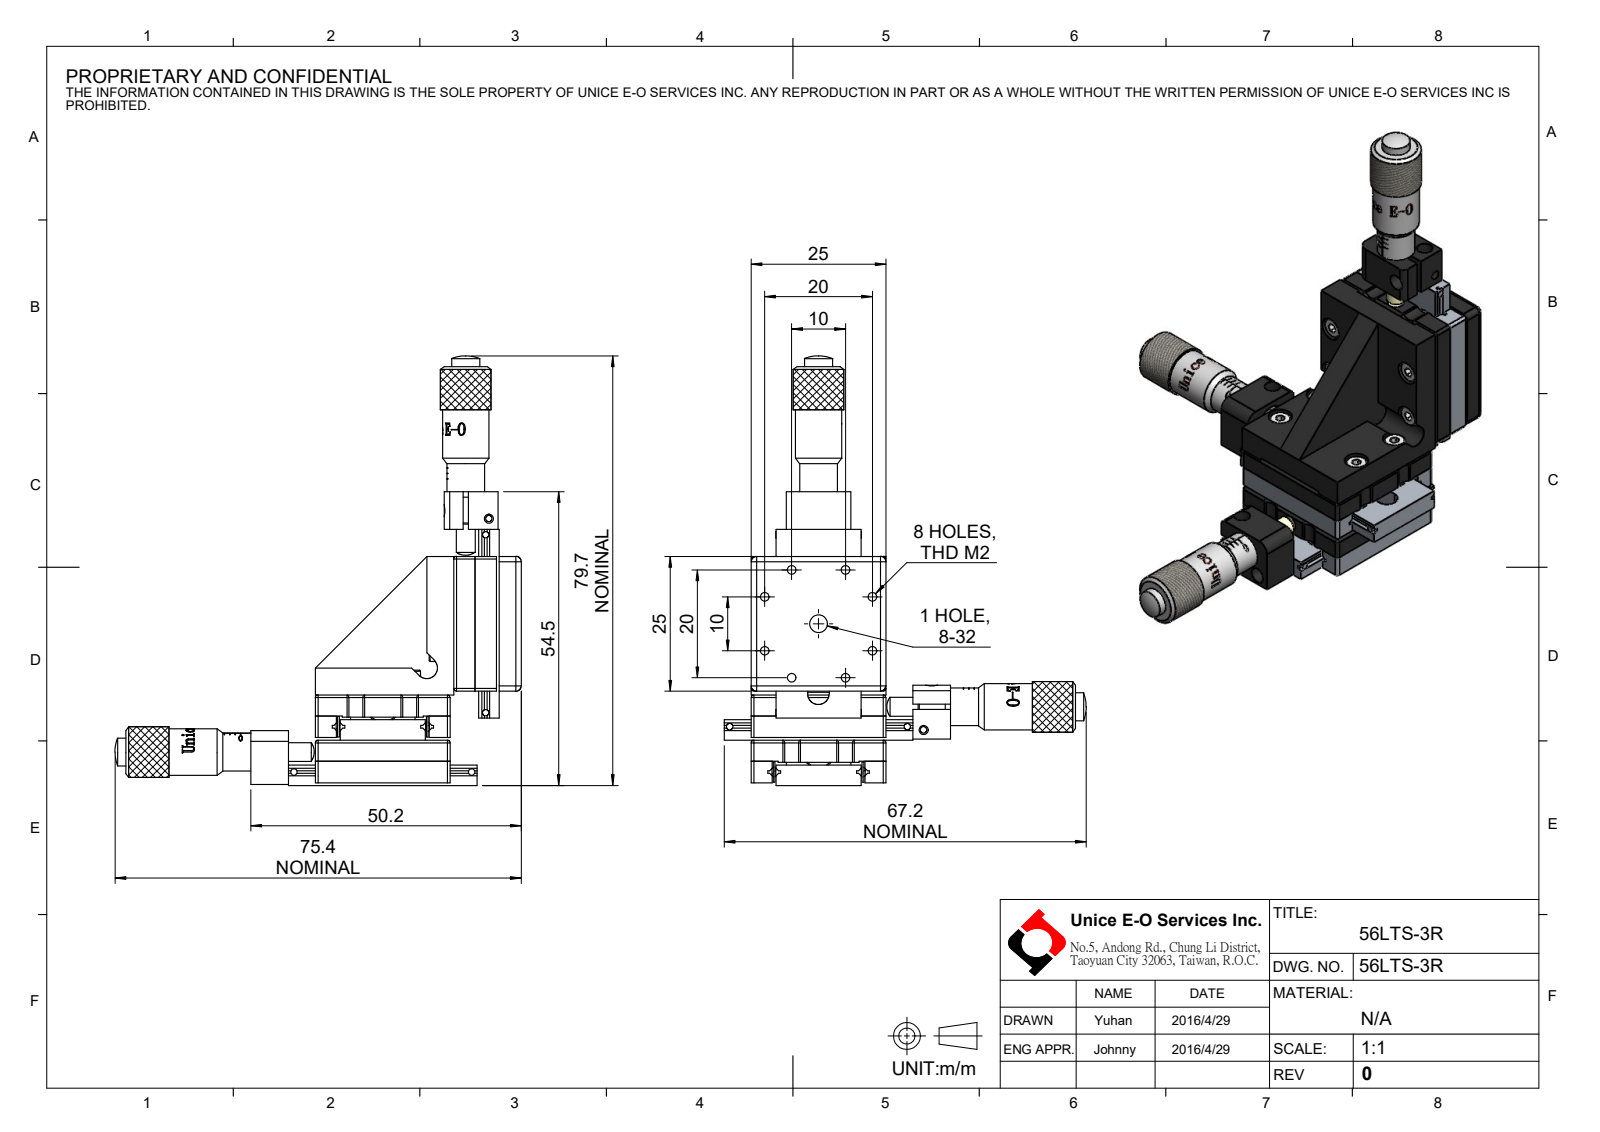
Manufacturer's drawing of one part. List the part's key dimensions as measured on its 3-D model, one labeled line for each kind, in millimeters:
Part name (STEP PRODUCT): 56LTS-3R
STEP written by: SolidWorks 2016 (CONFIG_CONTROL_DESIGN)
Units: millimetres
Bodies: 73 solids, 2750 faces (1124 planar, 1026 cylindrical, 600 other)
Overall size (bounding box): 79.7 × 75.4 × 67.2
Volume: 28 678 mm³ · Surface area: 30 420 mm²
Round holes (diameter × count): ⌀1.1 ×30, ⌀1.8 ×27, ⌀3.1 ×18, ⌀1.6 ×16, ⌀2.4 ×16, ⌀1.2 ×12, ⌀3 ×12, ⌀4 ×12, ⌀4.4 ×8, ⌀1.7 ×3, ⌀2.5 ×3, ⌀2.6 ×3
Round bosses / shafts (diameter × count): ⌀1.5 ×35, ⌀2 ×8, ⌀4 ×4, ⌀9.4 ×3, ⌀8.6 ×3, ⌀7 ×3, ⌀6.4 ×3, ⌀5.7 ×3
Partial cylindrical surfaces — rounded edges, fillets, slot ends (radius × count): R0.5 ×44, R2 ×22, R0.75 ×14, R1 ×11, R4.28 ×3
Main face-to-face distances: 8.4, 4.6, 0.5, 8.9, 4.5, 0.7, 4.1, 4.3, 3.8, 3.9
Hole centre spacings: 11.18, 15.81, 4.04, 5.03, 5.64, 9, 11.44, 13.87
